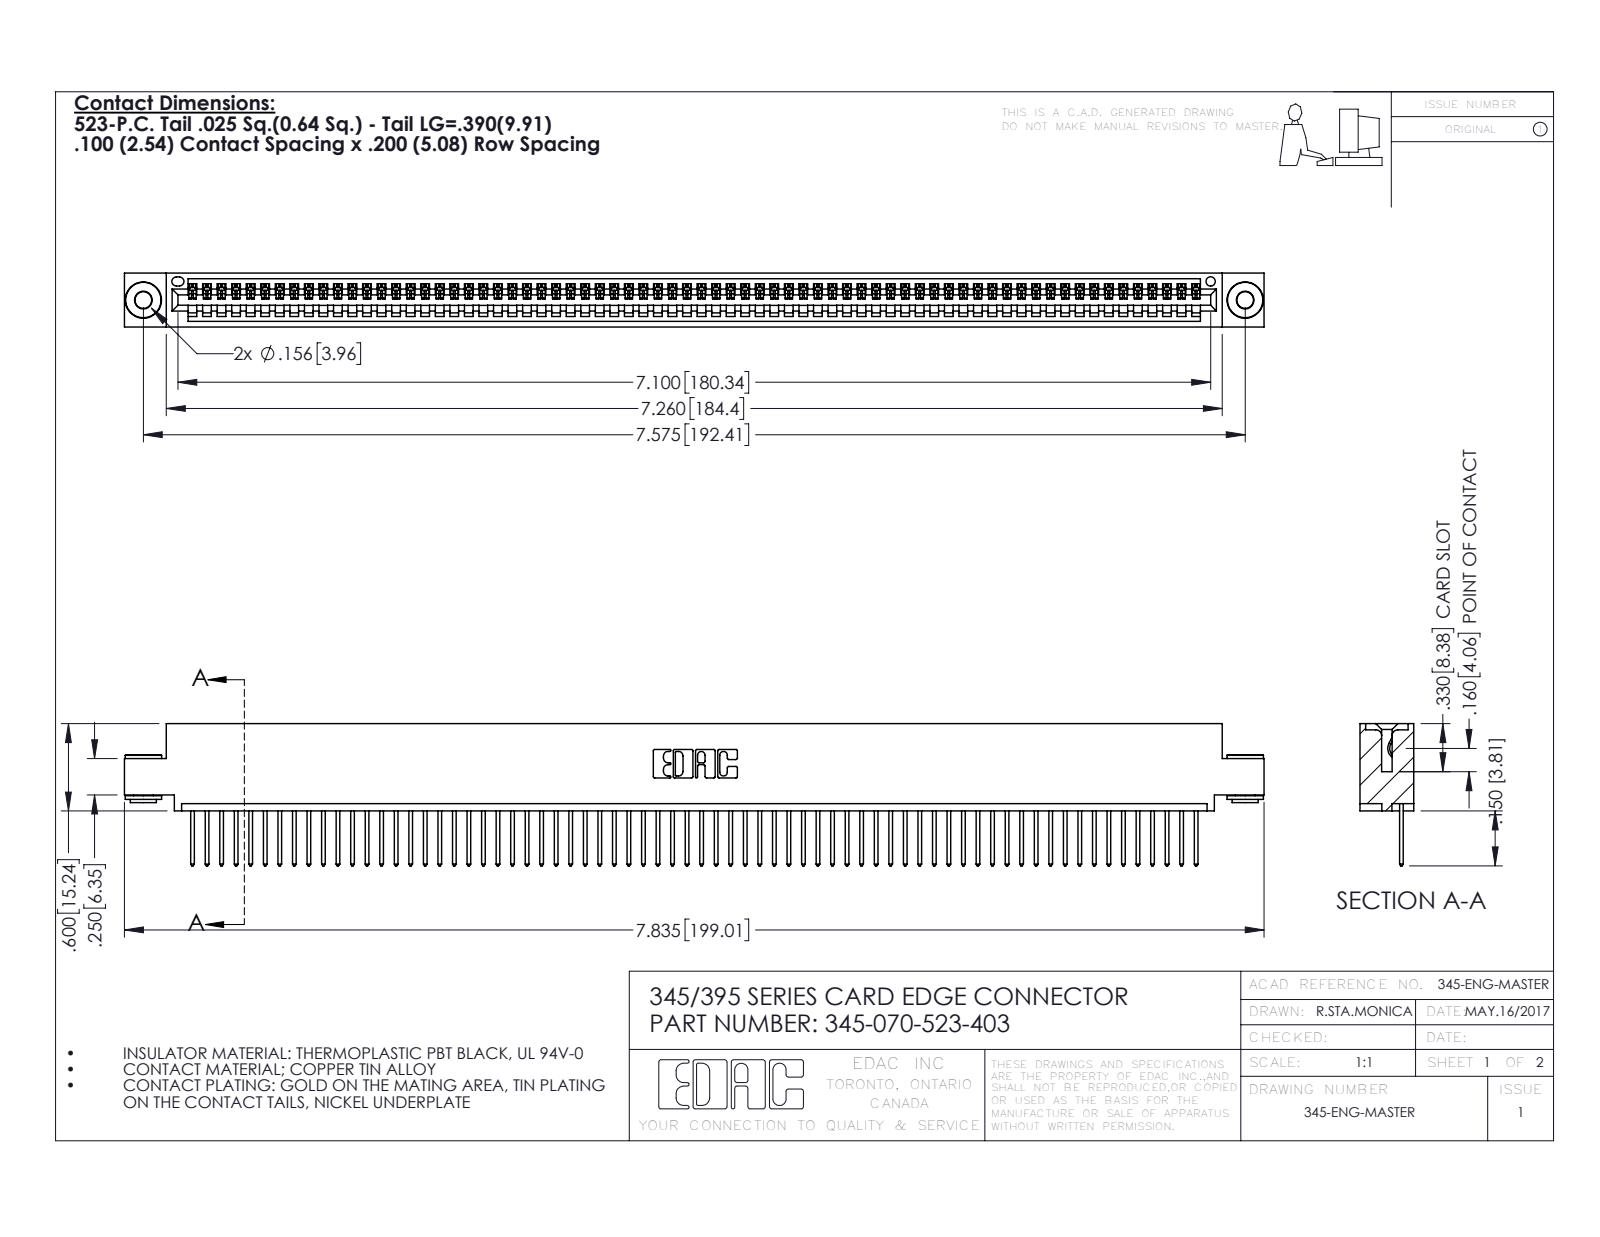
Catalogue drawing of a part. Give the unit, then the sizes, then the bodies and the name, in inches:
Units: inches
Overall size (bounding box): 7.835 × 0.977 × 0.37
Round holes (diameter × count): ⌀0.116 ×2, ⌀0.156 ×2, ⌀0.064 ×1
Round bosses / shafts (diameter × count): ⌀0.25 ×2, ⌀0.18 ×2, ⌀0.136 ×2
Partial cylindrical surfaces — rounded edges, fillets, slot ends (radius × count): R0.006 ×140, R0.01 ×140, R0.01 ×22, R0.007 ×6, R0.031 ×6, R0.026 ×3, R0.031 ×2, R0.04 ×2
Main face-to-face distances: 0.072, 0.298, 0.37, 0.025, 0.2, 0.098, 0.272, 0.225, 0.149, 0.072
Hole centre spacings: 0.27, 7.339, 7.575
Volume: 1.163 in³ · Surface area: 40.41 in²
Bodies: 73 solids, 4228 faces (2894 planar, 1326 cylindrical, 8 other)
Part name (STEP PRODUCT): 345-070-523-403; 345 Part_0.110 Offset - 0.156 Dia-TH; 345-250-002_345-250-002-102; 345-292-001_345-293-123
STEP written by: SolidWorks 2016 (CONFIG_CONTROL_DESIGN)
